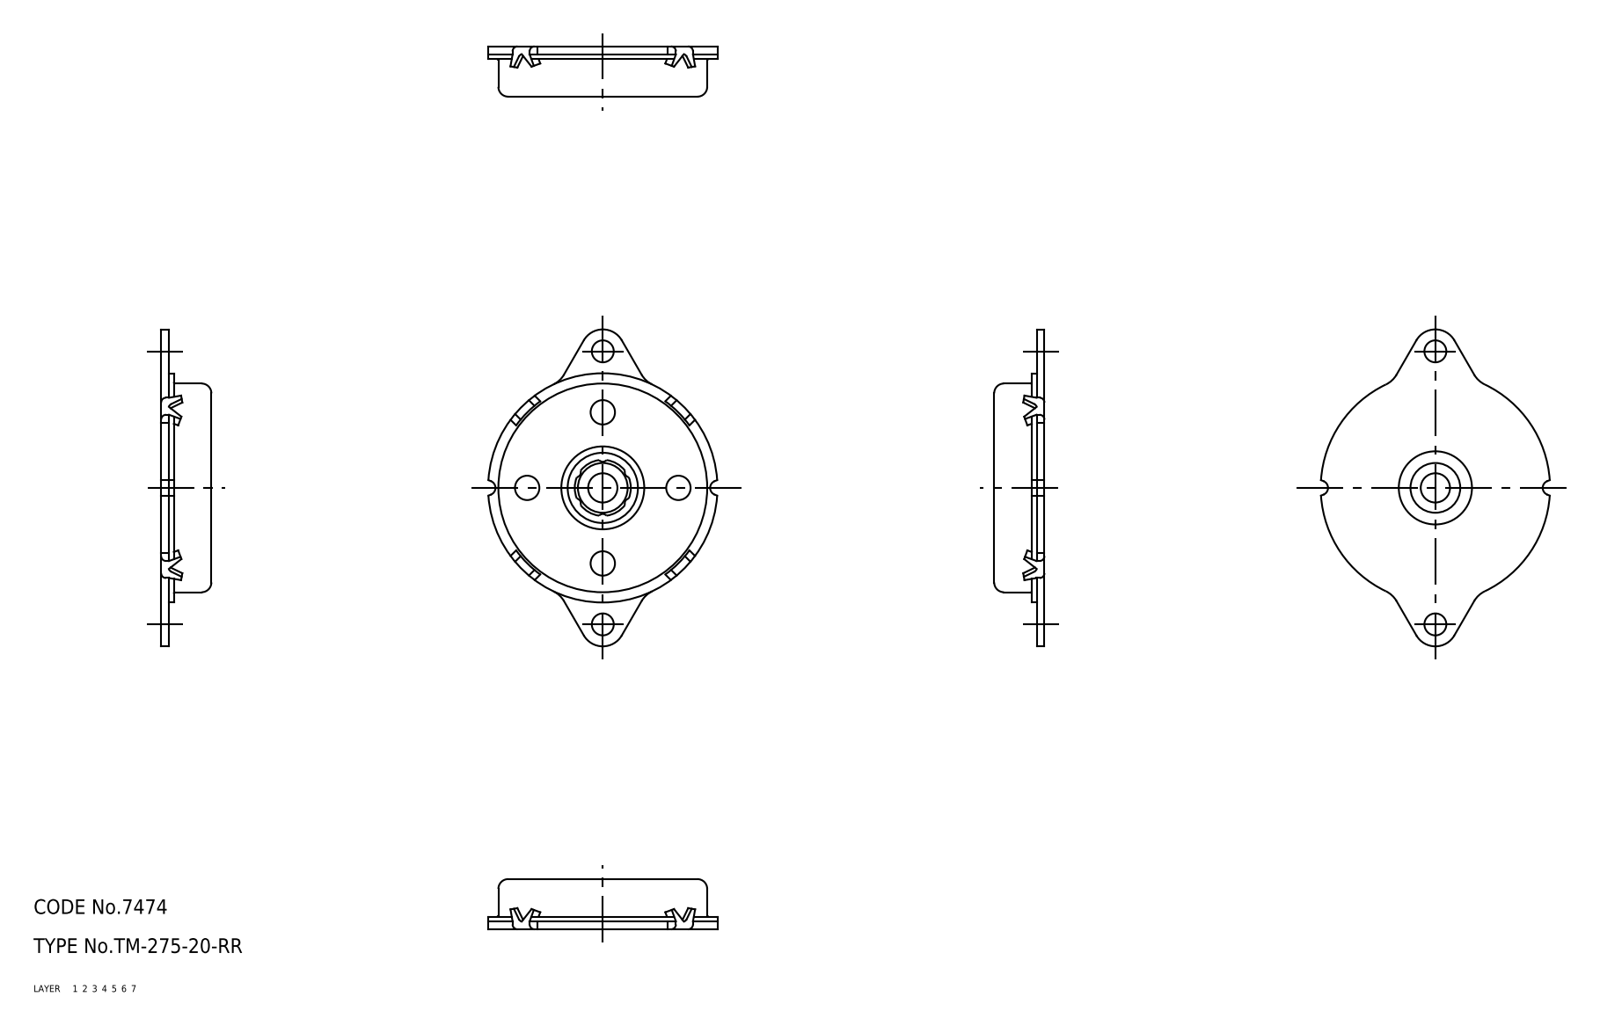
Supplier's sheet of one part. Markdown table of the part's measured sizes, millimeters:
| quantity | value |
| --- | --- |
| part name | inner ring; TM_275_20_RR_1151_36 |
| STEP written by | CADfix (AUTOMOTIVE_DESIGN) |
| units | millimeters |
| bodies | 2 solids, 169 faces (0 planar, 0 cylindrical, 169 other) |
| overall size | 65 × 46.89 × 10.3 |
| volume | 15 252 mm³ |
| surface area | 6 866 mm² |
